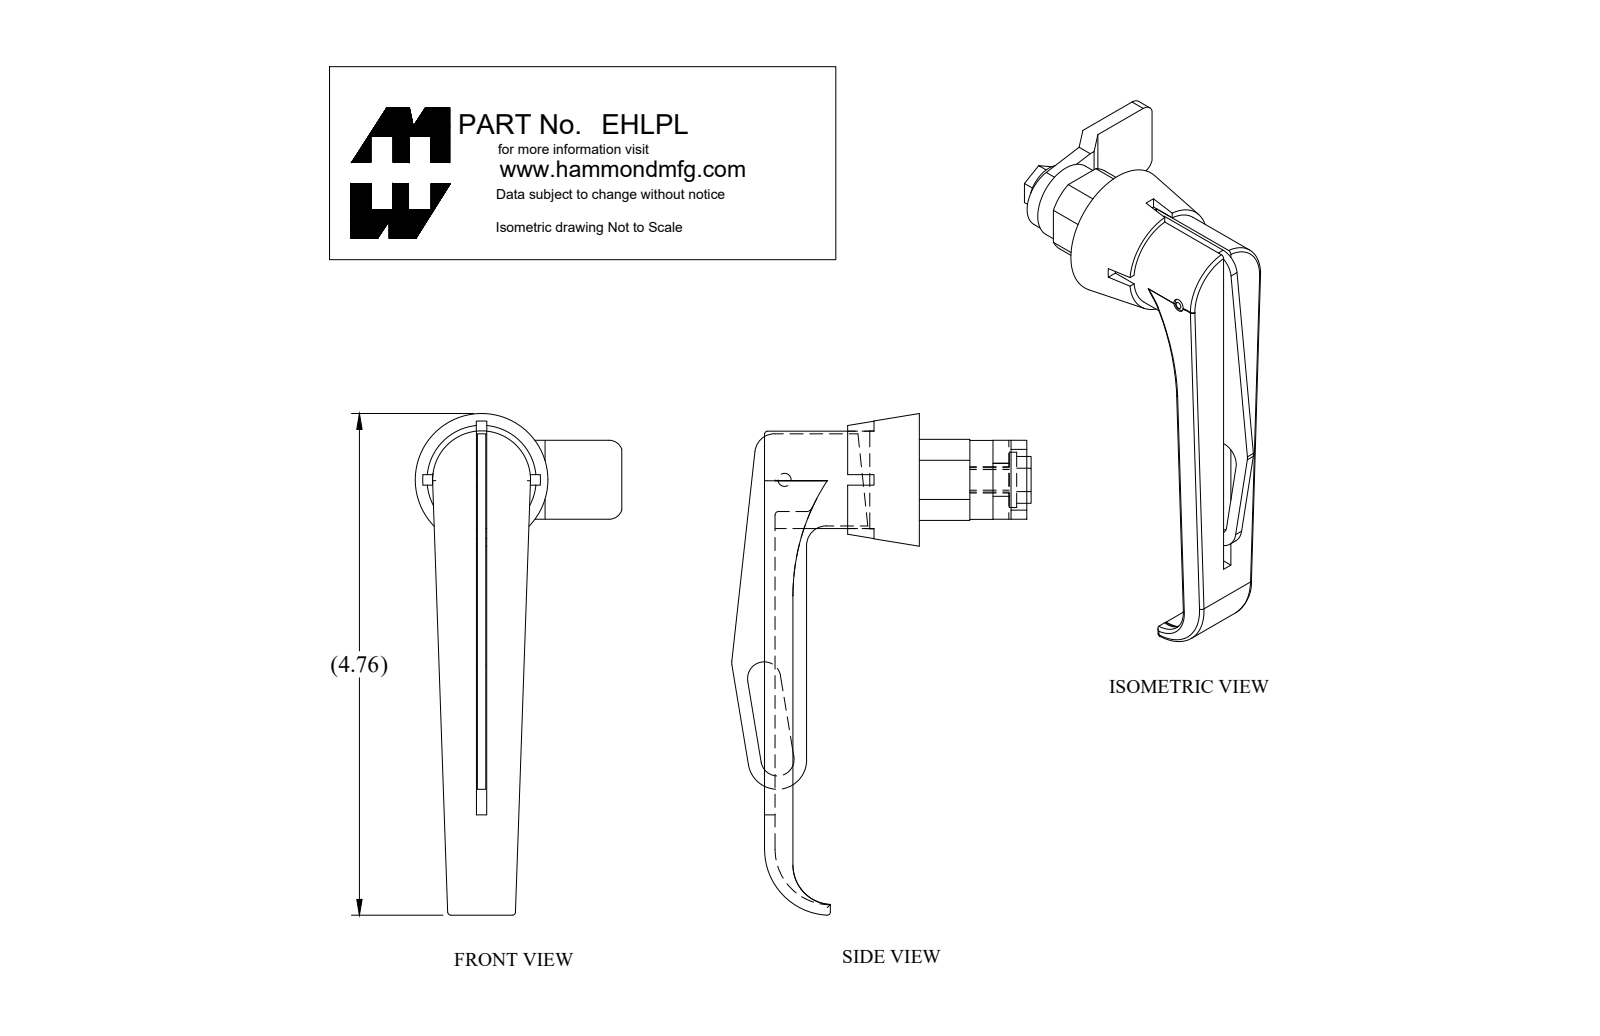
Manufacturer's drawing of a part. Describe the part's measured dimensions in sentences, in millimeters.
The part is named "EHLPL_Default". Its 3-D file was written by "SolidWorks 2018 (CONFIG_CONTROL_DESIGN)". It is 4 solids with 158 faces: 83 planar, 49 cylindrical and 26 other. Overall it measures 121 by 72.3 by 49.8 millimeters. Its volume is 37 760 cubic millimeters and its surface area 19 100 square millimeters. Round holes: 1 of diameter 3.2, 1 of diameter 5. Round bosses or shafts: 1 of diameter 23.6, 1 of diameter 19.1, 1 of diameter 13.3, 1 of diameter 5.9. Partial cylindrical surfaces (rounded edges, fillets, slot ends): 13 of radius 0.8, 3 of radius 3.2, 2 of radius 4.7, 2 of radius 9.5, 2 of radius 50.8, 1 of radius 4, 1 of radius 4, 1 of radius 7.1. The main face-to-face distances are 2.3, 2.5, 2, 2.5, 3.8, 4.3, 34.8, 37.4, 17.8, 52.6.
